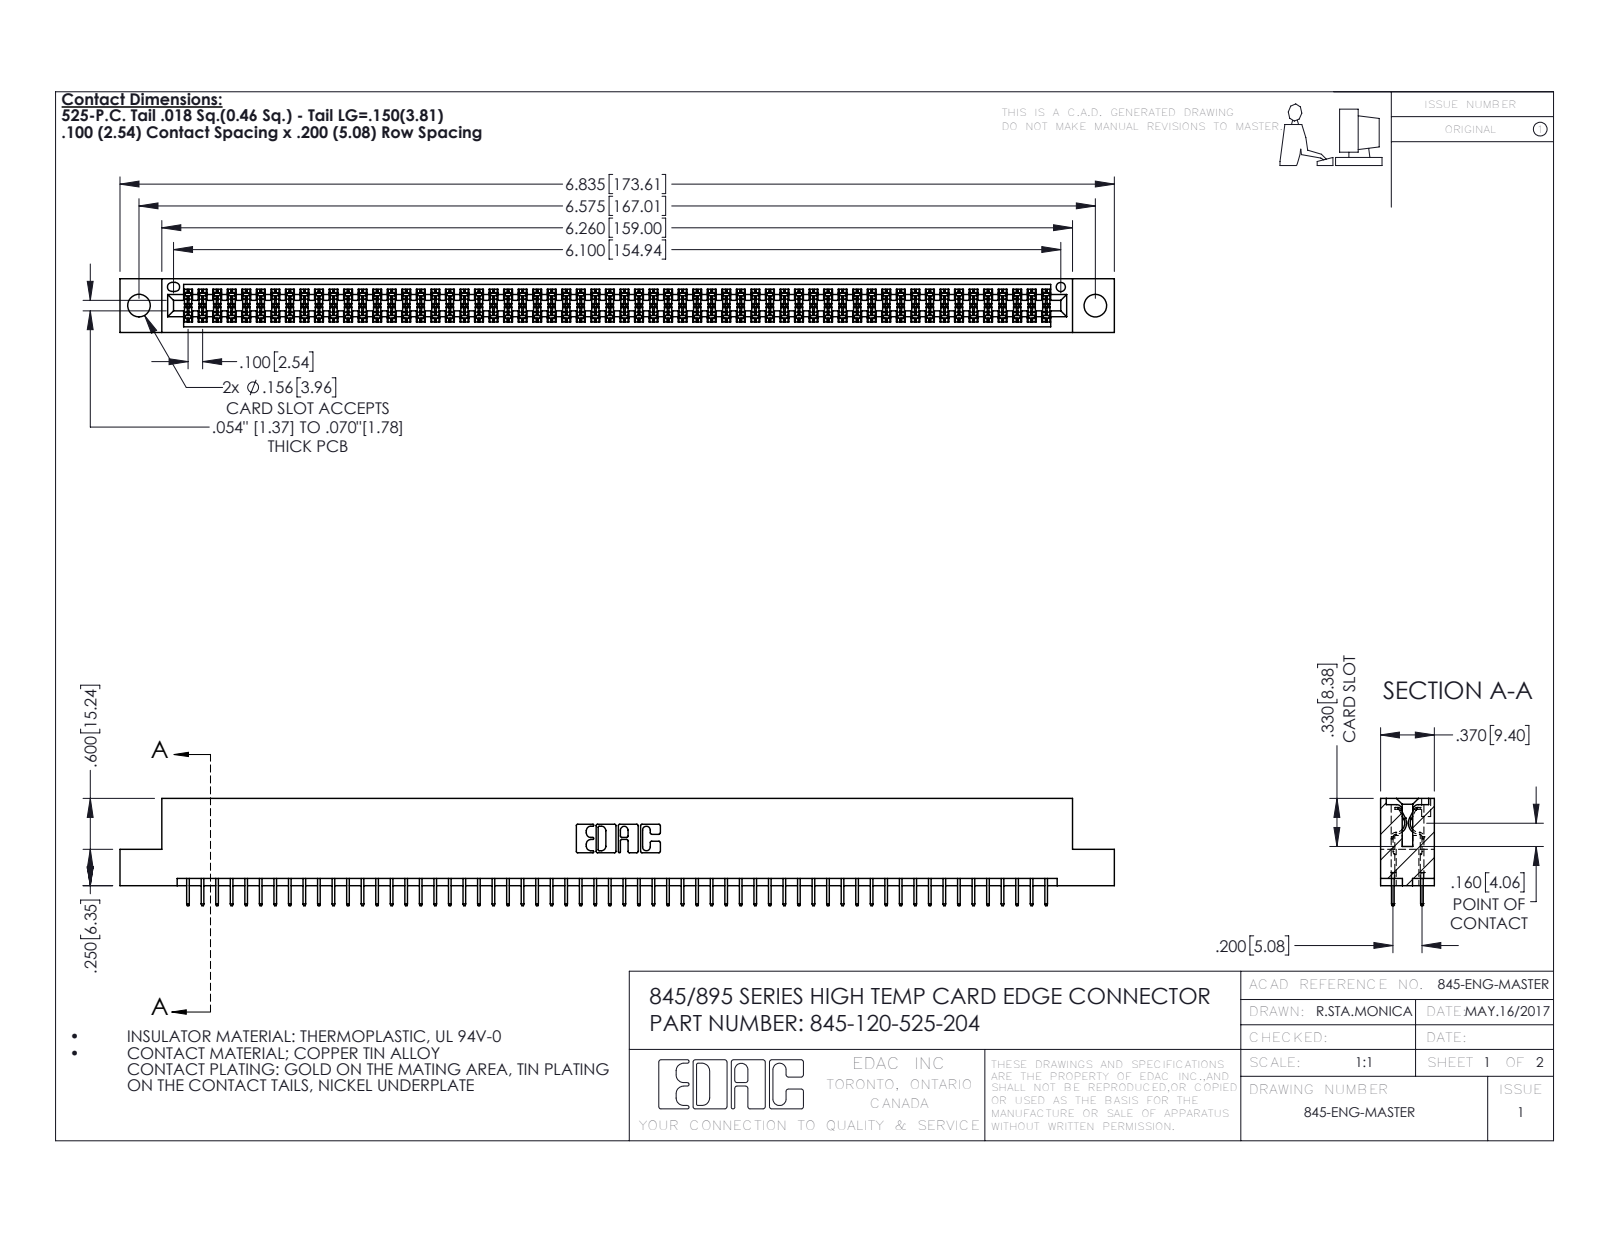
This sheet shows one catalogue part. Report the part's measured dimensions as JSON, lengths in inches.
{"part_name": "845 Part_Flush Mounting Lugs - 0.156 Dia-TH; 345-292-001_345-293-125; 845-120-525-204", "step_written_by": "SolidWorks 2020 (CONFIG_CONTROL_DESIGN)", "units": "inches", "bodies": {"solids": 121, "faces": 6606, "planar": 4760, "cylindrical": 1846, "other": 0}, "overall_size": [6.835, 0.737, 0.37], "volume_in3": 1.022, "surface_area_in2": 37.7, "round_holes": [[0.156, 2], [0.064, 1]], "partial_cylinders_radius": [[0.006, 180], [0.01, 22], [0.007, 6], [0.031, 6], [0.026, 3], [0.014, 2], [0.019, 2], [0.022, 2]], "face_to_face_distances": [0.298, 0.072, 0.2, 0.37, 0.098, 0.272, 0.025, 0.225, 0.072, 0.175], "hole_center_spacings": [0.27, 6.339, 6.575]}
